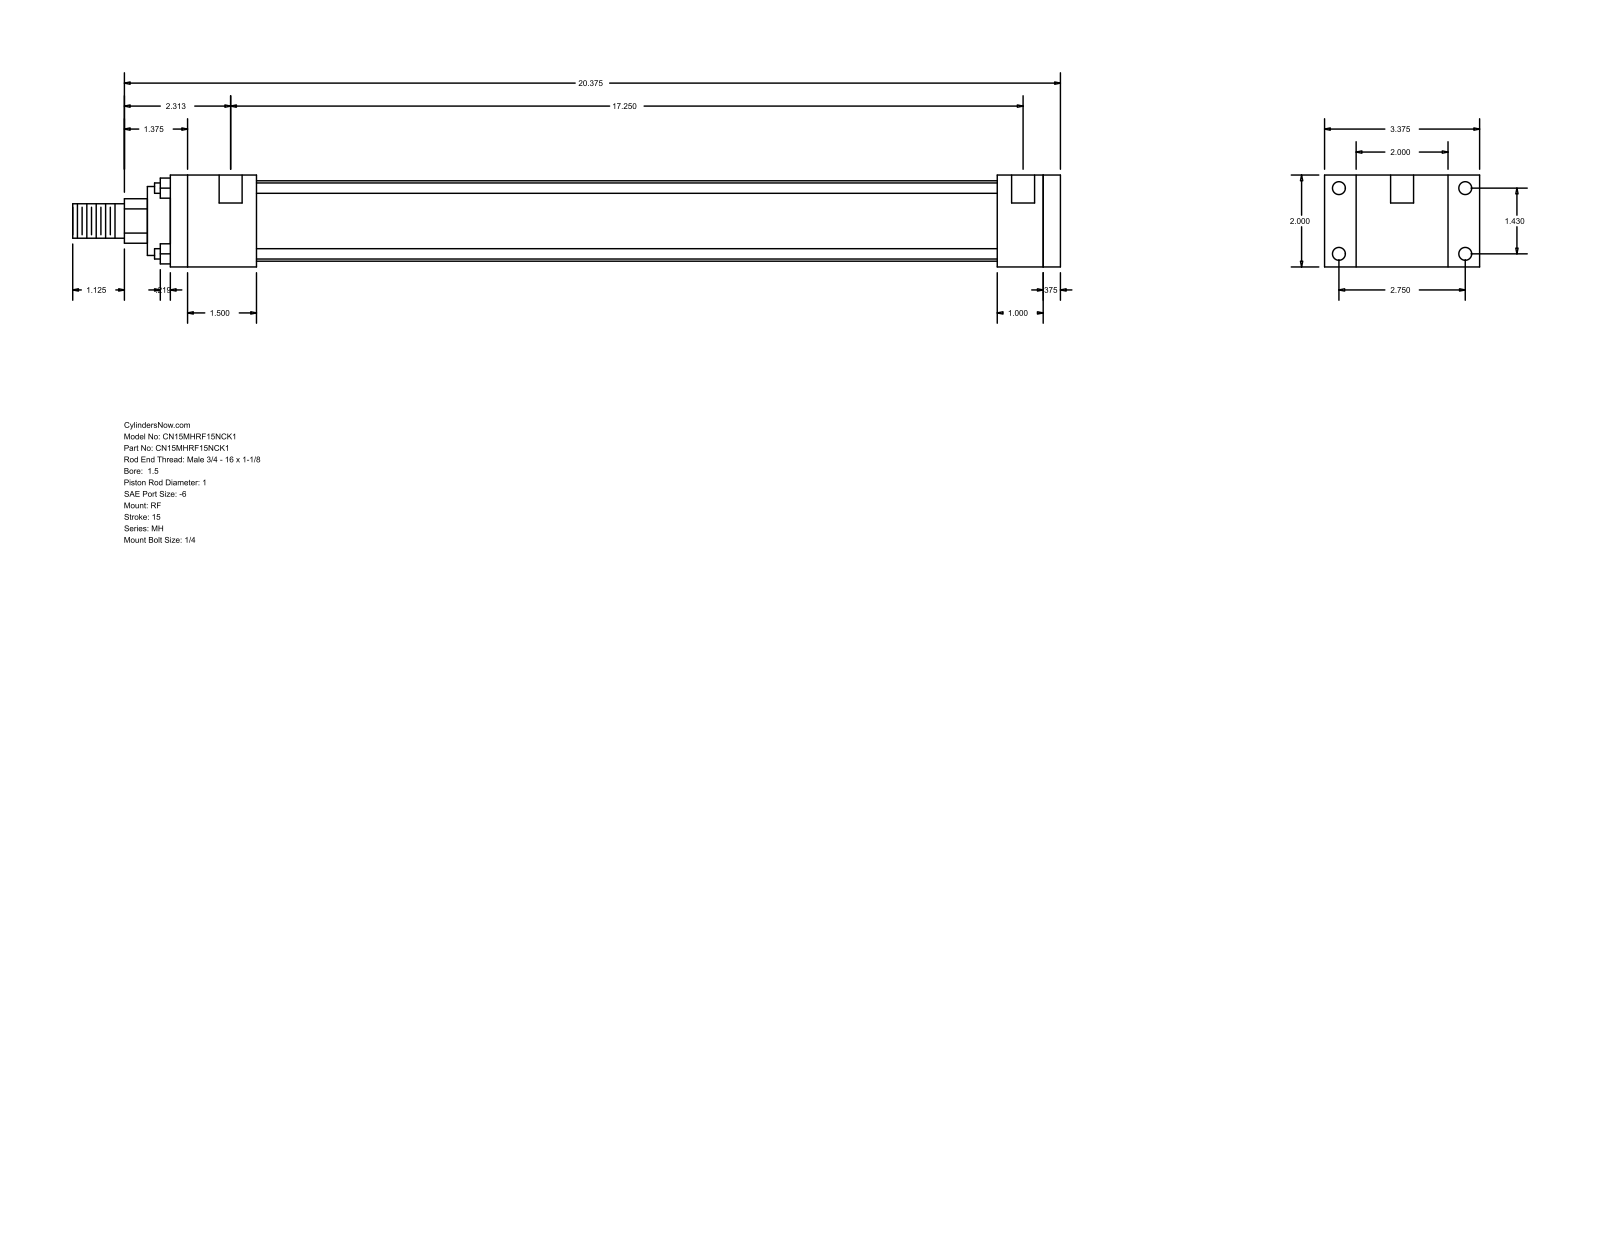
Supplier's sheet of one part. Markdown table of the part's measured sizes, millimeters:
| quantity | value |
| --- | --- |
| part name | MH_RF__0150_1 |
| STEP written by | GSSL Pune (CONFIG_CONTROL_DESIGN) |
| units | millimeters |
| bodies | 0 solids, 92 faces (64 planar, 28 cylindrical, 0 other) |
| overall size | 546.1 × 85.72 × 50.8 |
| round holes (diameter × count) | 5.56 × 4, 7.14 × 4, 12.7 × 2 |
| round bosses / shafts (diameter × count) | 5.71 × 4, 44.45 × 1, 38.1 × 1, 25.4 × 1, 19.05 × 1 |
| partial cylindrical surfaces (radius × count) | 12.29 × 1 |
| main face-to-face distances | 50.8, 9.52, 482.6, 25.4, 492.12, 17.46, 68.26, 457.2, 34.92, 47.63 |
| hole center spacings | 36.32, 69.84, 78.72, 441.33, 3.18, 438.15 |
